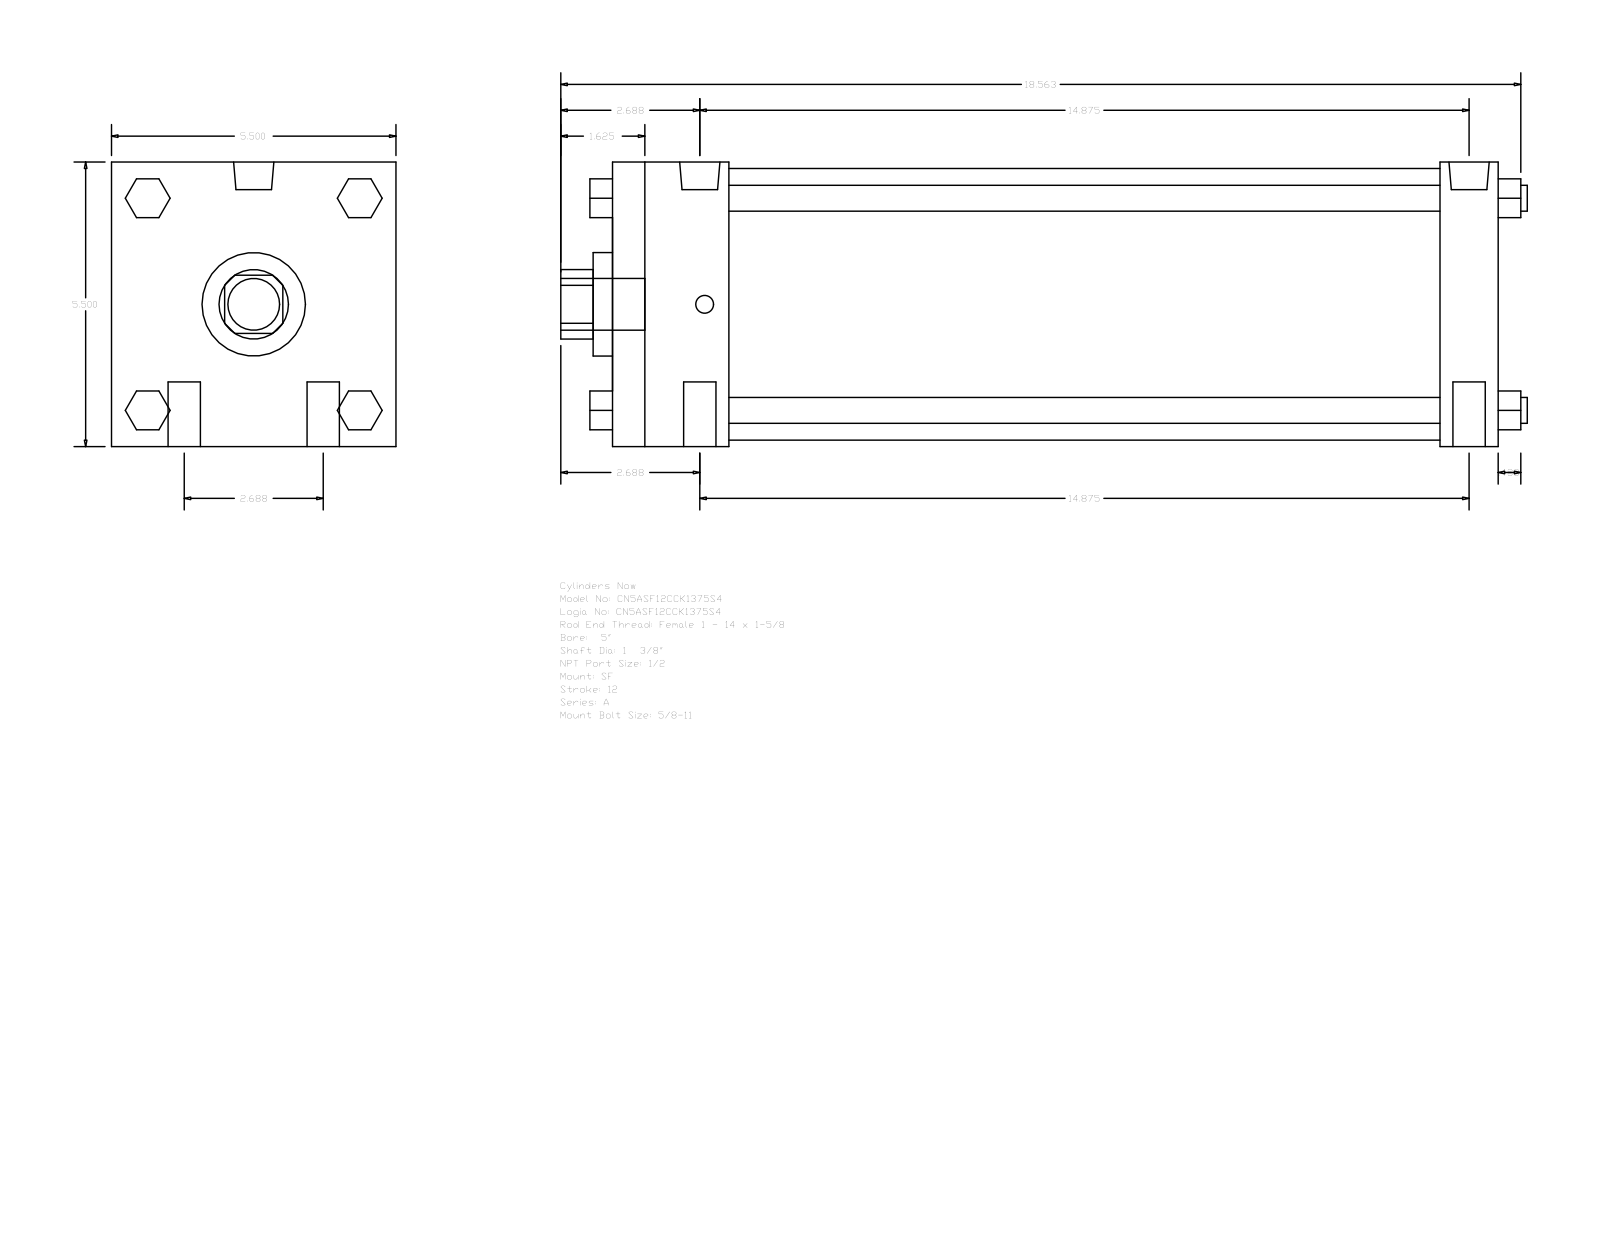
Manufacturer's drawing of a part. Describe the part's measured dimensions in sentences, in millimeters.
The part is named "A_SF__0500_1.375". Its 3-D file was written by "GSSL Pune (CONFIG_CONTROL_DESIGN)". It is 0 solids with 124 faces: 94 planar, 30 cylindrical and 0 other. Overall it measures 474.66 by 139.7 by 139.7 millimeters. Round holes: 1 of diameter 34.92, 1 of diameter 50.8, 1 of diameter 133.35. Round bosses or shafts: 4 of diameter 15.88, 4 of diameter 12.7, 2 of diameter 19.77, 2 of diameter 8.73, 1 of diameter 25.4. Partial cylindrical surfaces (rounded edges, fillets, slot ends): 1 of radius 17.06. The main face-to-face distances are 139.7, 434.98, 28.58, 57.15, 406.4, 349.25, 377.83, 19.05, 52.07, 90.18.
